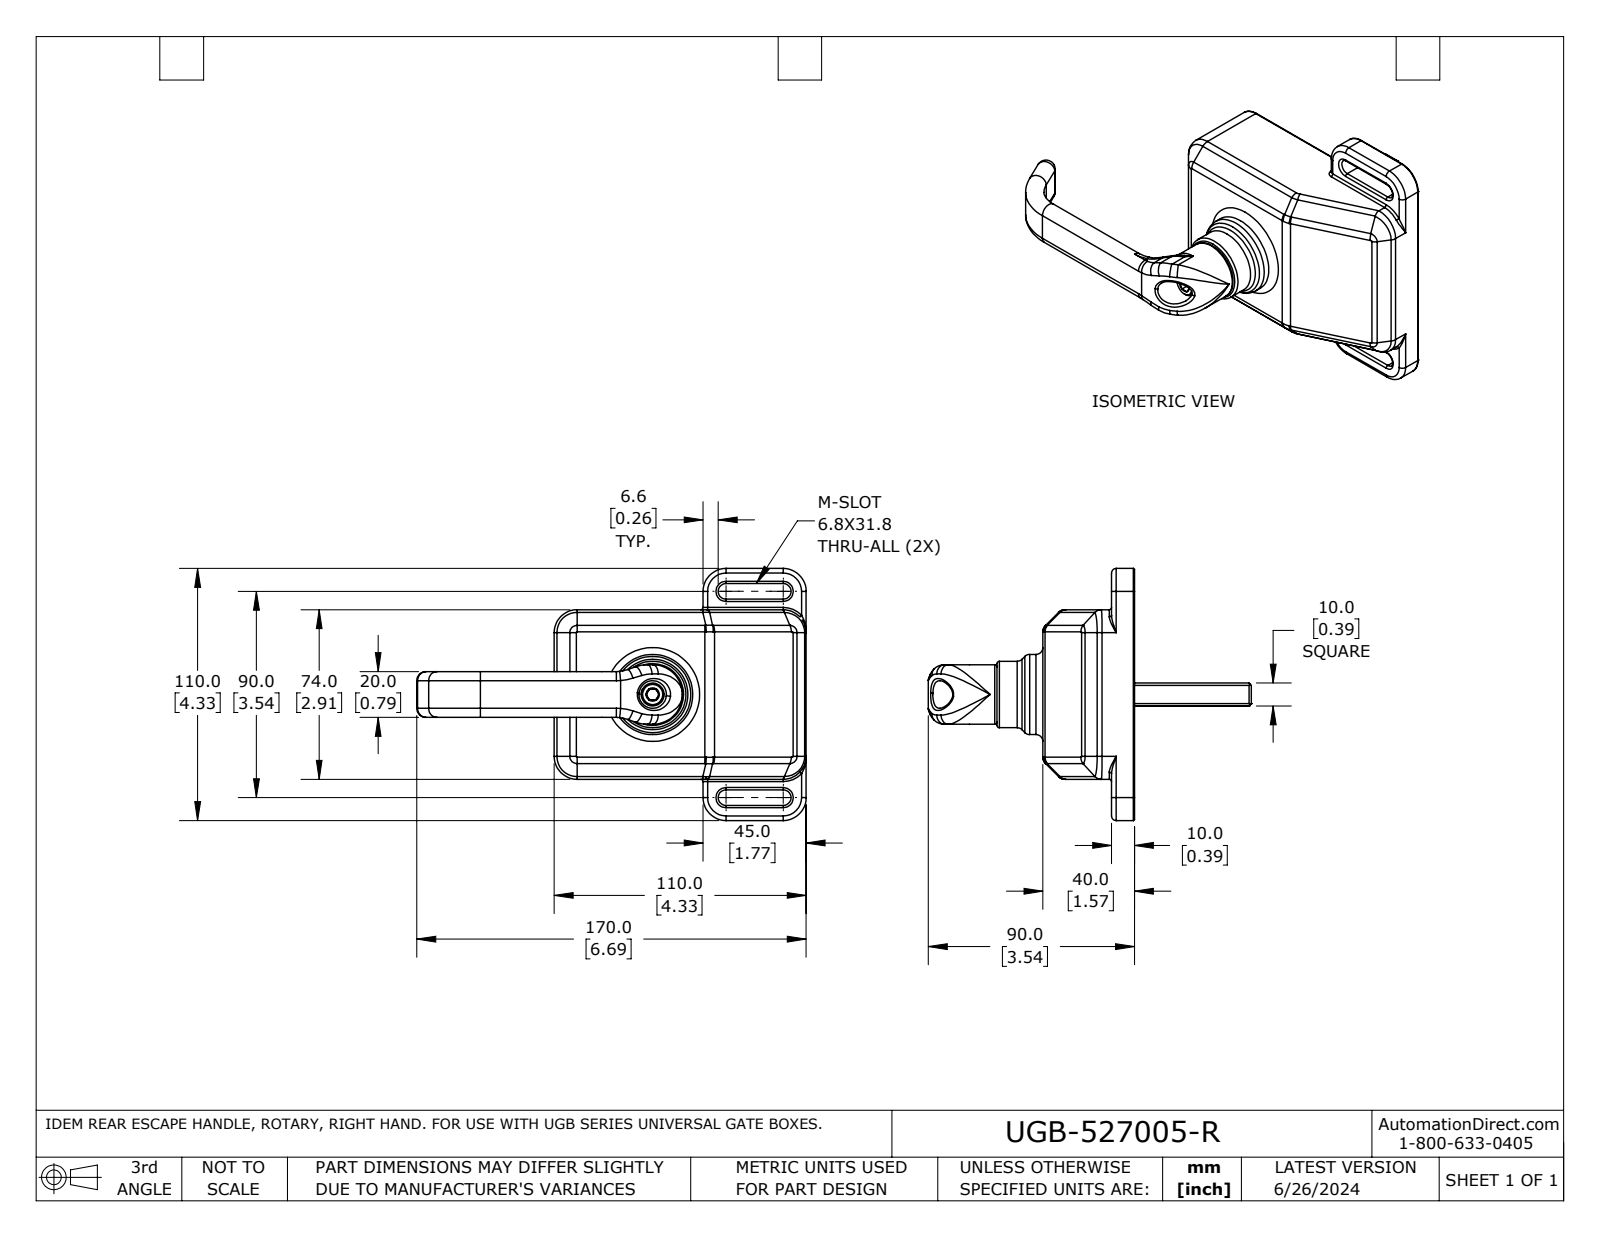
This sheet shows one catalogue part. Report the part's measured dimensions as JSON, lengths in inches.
{"part_name": "UGB-527005-R", "step_written_by": "SolidWorks 2023 (AUTOMOTIVE_DESIGN)", "units": "inches", "bodies": {"solids": 10, "faces": 783, "planar": 219, "cylindrical": 291, "other": 273}, "overall_size": [6.693, 5.551, 4.331], "volume_in3": 8.996, "surface_area_in2": 126.8, "round_holes": [[0.165, 4], [0.217, 4], [0.26, 1], [0.268, 1], [0.472, 1], [0.827, 1], [0.882, 1], [0.984, 1]], "round_bosses_or_shafts": [[0.335, 4], [0.197, 4], [0.173, 4], [1.378, 1], [1.142, 1], [1.024, 1], [0.787, 1], [0.394, 1]], "partial_cylinders_radius": [[0.039, 93], [0.02, 61], [0.157, 17], [0.394, 11], [0.079, 8], [0.134, 4], [0.177, 4], [0.236, 4]], "face_to_face_distances": [0.118, 0.079, 2.795, 1.457, 2.677, 1.417, 0.039, 0.315, 0.236, 2.913], "hole_center_spacings": [1.679, 2.126, 2.483, 3.543, 4.132]}
